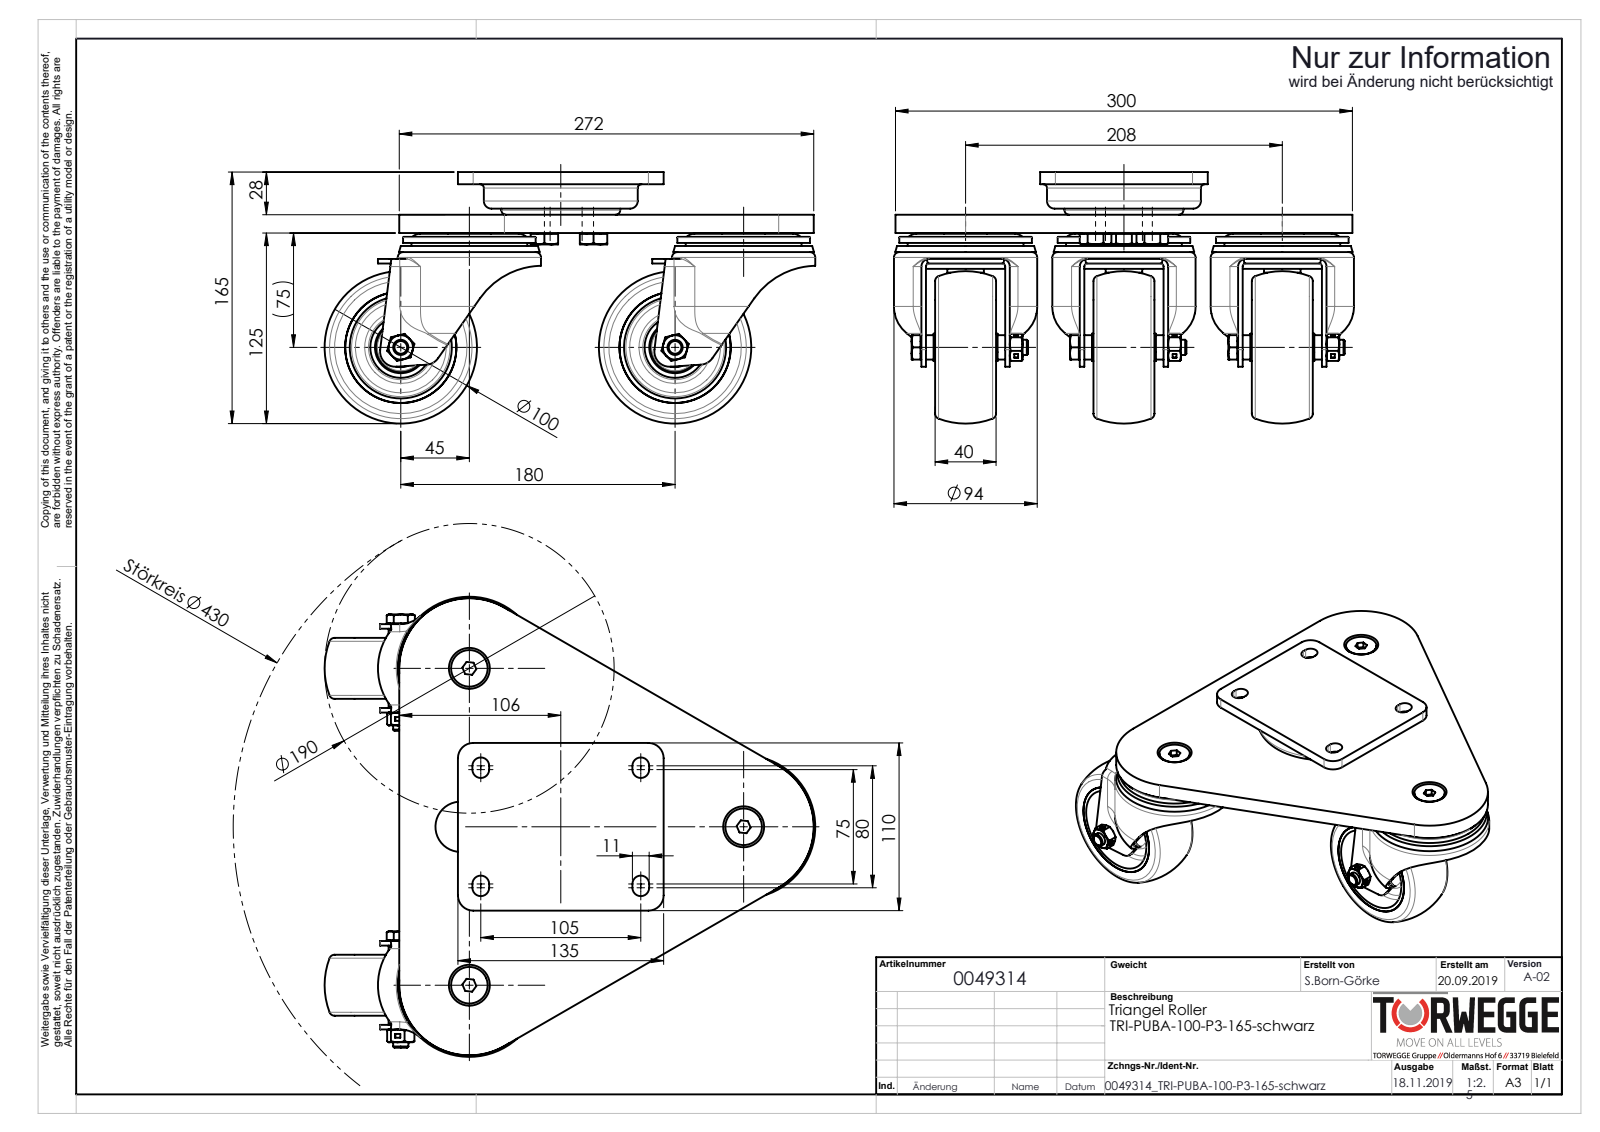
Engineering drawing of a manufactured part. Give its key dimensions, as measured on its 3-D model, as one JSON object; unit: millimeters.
{"part_name": "0049314_TRI-PUBA-100-P3-165-schwarz_(A-02)", "step_written_by": "SolidWorks 2018 (AUTOMOTIVE_DESIGN)", "units": "millimeters", "bodies": {"solids": 62, "faces": 1452, "planar": 468, "cylindrical": 411, "other": 573}, "overall_size": [322, 301.85, 165], "volume_mm3": 1960000, "surface_area_mm2": 538294, "round_holes": [[12, 7], [10.2, 6], [12.7, 3], [13, 3], [13.5, 3], [30, 3], [88, 3], [8.5, 2], [10, 2], [10.02, 2], [10.1, 2], [12.4, 2]], "round_bosses_or_shafts": [[18, 5], [94, 3], [87, 3], [76, 3], [62, 3], [28.5, 3], [24, 3], [11.79, 3]], "partial_cylinders_radius": [[5, 9], [5.5, 8], [10, 8], [2, 6], [41.04, 3], [46, 3], [14, 2], [50, 2]], "face_to_face_distances": [12, 40, 103.92, 28, 6, 9, 207.84, 49, 55.5, 3], "hole_center_spacings": [132.07, 37.24, 98.5, 207.84, 180]}
